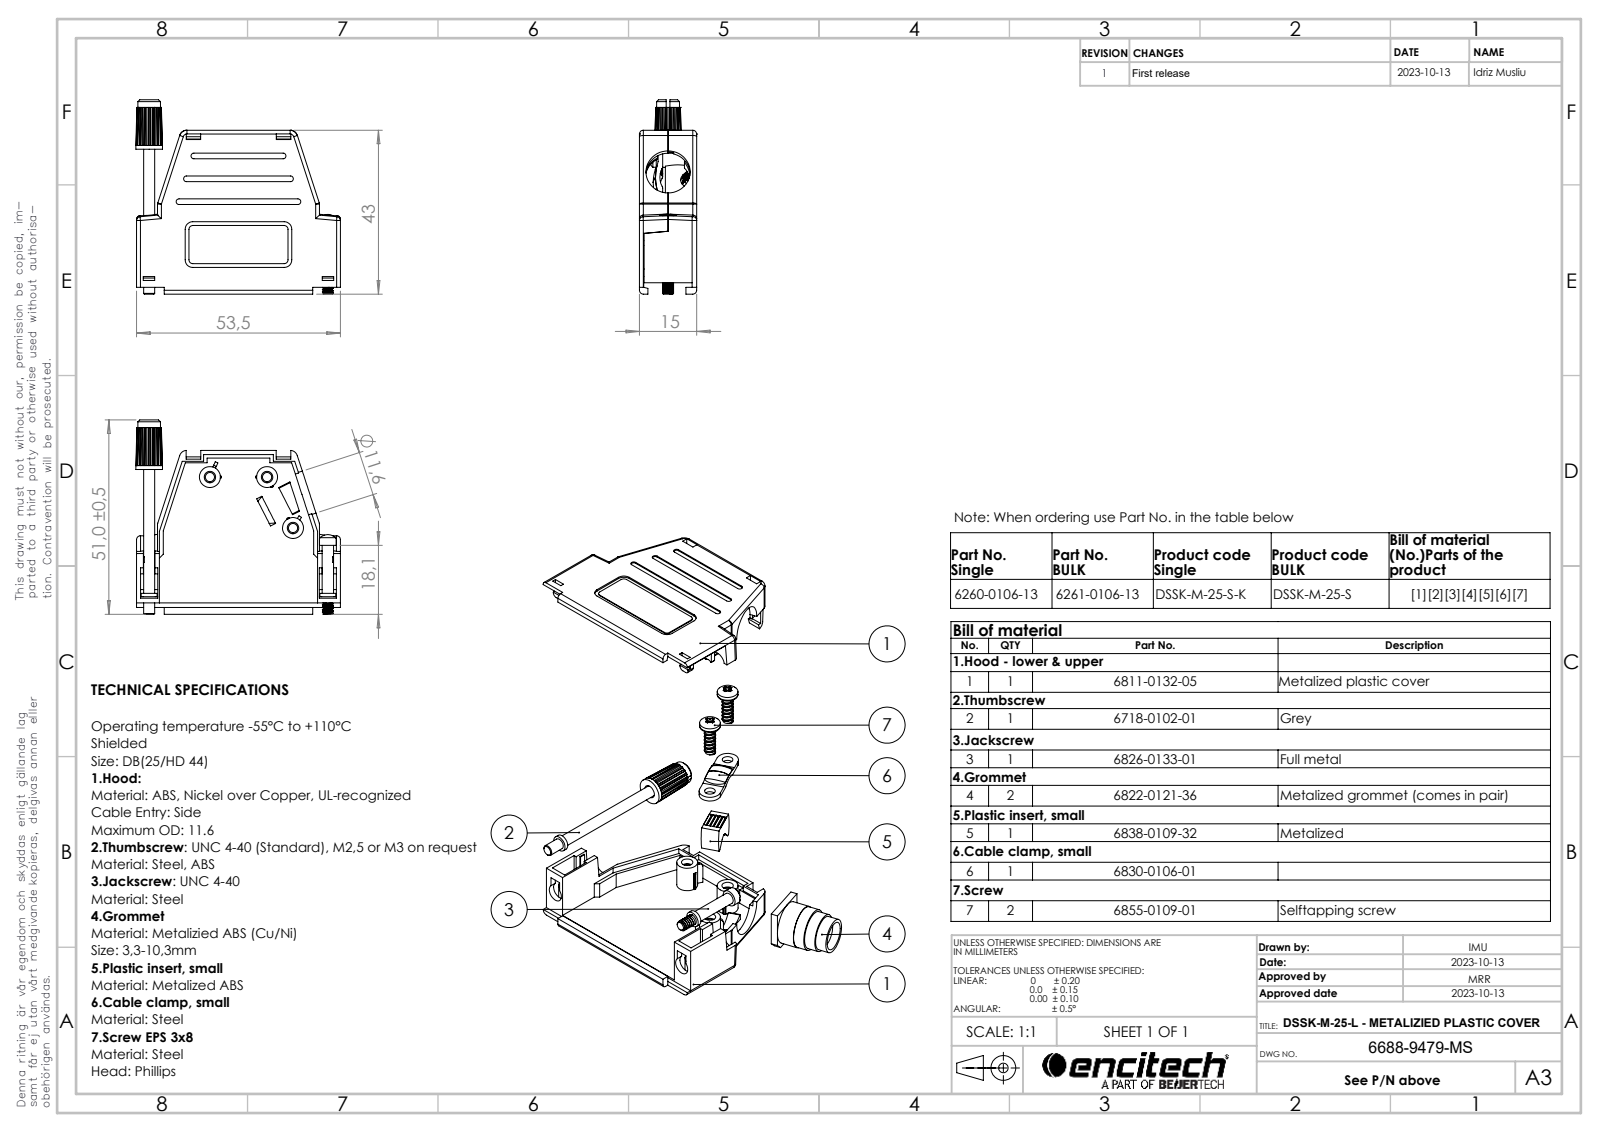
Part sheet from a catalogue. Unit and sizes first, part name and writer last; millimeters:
Units: millimetres
Overall size (bounding box): 58.04 × 51 × 15
Round holes (diameter × count): ⌀2.4 ×3, ⌀3 ×3, ⌀2.8 ×2, ⌀3.5 ×1, ⌀7.5 ×1, ⌀8.5 ×1, ⌀9.5 ×1, ⌀10.5 ×1, ⌀11.6 ×1
Round bosses / shafts (diameter × count): ⌀5.5 ×3, ⌀5.45 ×2, ⌀4.2 ×2, ⌀2.46 ×2, ⌀11.3 ×1, ⌀11.1 ×1, ⌀10.1 ×1, ⌀9.1 ×1
Partial cylindrical surfaces — rounded edges, fillets, slot ends (radius × count): R1 ×40, R2 ×14, R0.75 ×6, R0.1 ×4, R0.25 ×4, R0.5 ×4, R1.5 ×3, R5.8 ×3
Main face-to-face distances: 13.3, 1.7, 11.6, 15, 1.5, 2, 14.8, 13.1, 5.8, 7.3
Hole centre spacings: 15, 7.57, 7.58, 18.9, 25.58
Volume: 11 175 mm³ · Surface area: 16 465 mm²
Bodies: 11 solids, 870 faces (570 planar, 219 cylindrical, 81 other)
Part name (STEP PRODUCT): 6822-0121-32; 6811-0132-05 Part 2; 6830-0106-01; 6811-0132-05 Part 1 (+5 more)
STEP written by: SolidWorks 2021 (AUTOMOTIVE_DESIGN)
